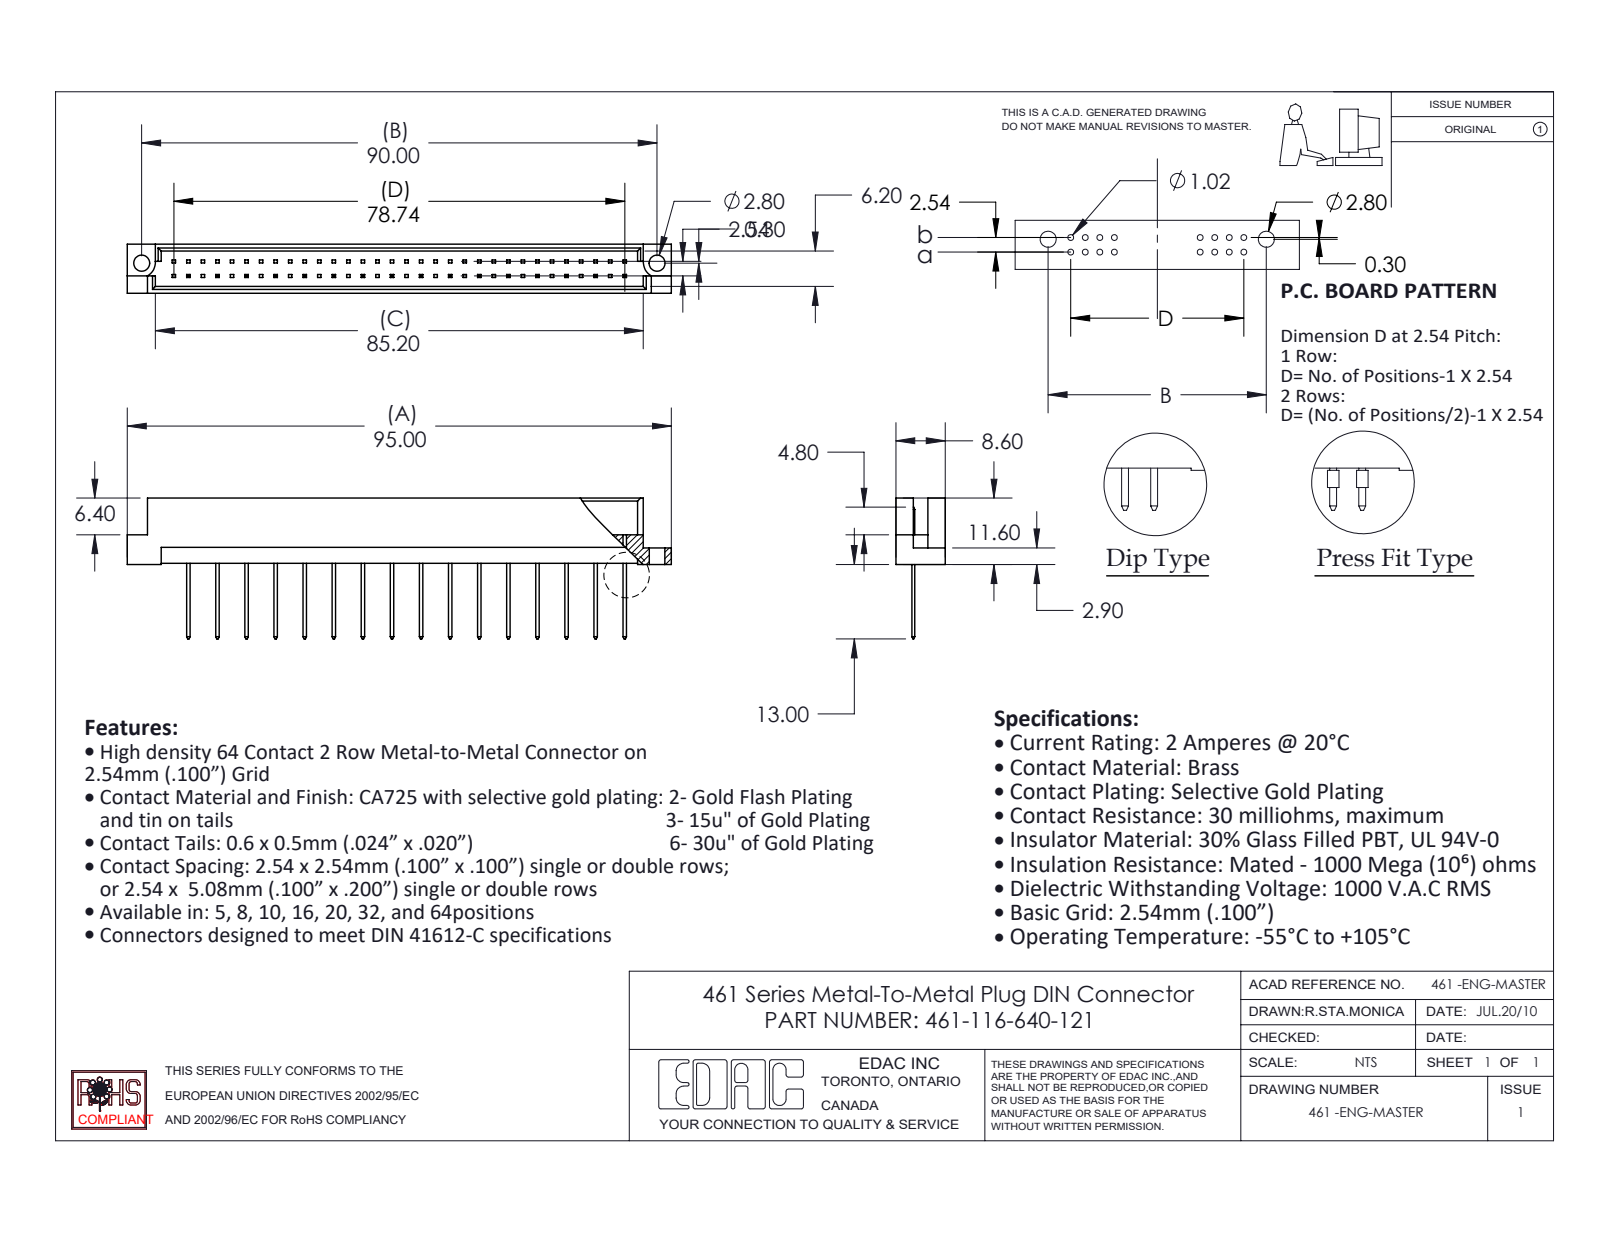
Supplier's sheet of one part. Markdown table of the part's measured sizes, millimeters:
| quantity | value |
| --- | --- |
| part name | 461-290_40; 461 Part_64; 461-116-640-221 |
| STEP written by | SolidWorks 2020 (CONFIG_CONTROL_DESIGN) |
| units | millimeters |
| bodies | 17 solids, 529 faces (522 planar, 7 cylindrical, 0 other) |
| overall size | 95 × 24.6 × 8.6 |
| volume | 4 765 mm³ |
| surface area | 6 475 mm² |
| round holes (diameter × count) | 2.8 × 2 |
| partial cylindrical surfaces (radius × count) | 2.8 × 2 |
| main face-to-face distances | 1.2, 7.4, 8.6, 6.2, 5, 3.28, 5.32, 2.08, 4.12, 2.78 |
| hole center spacings | 90 |
